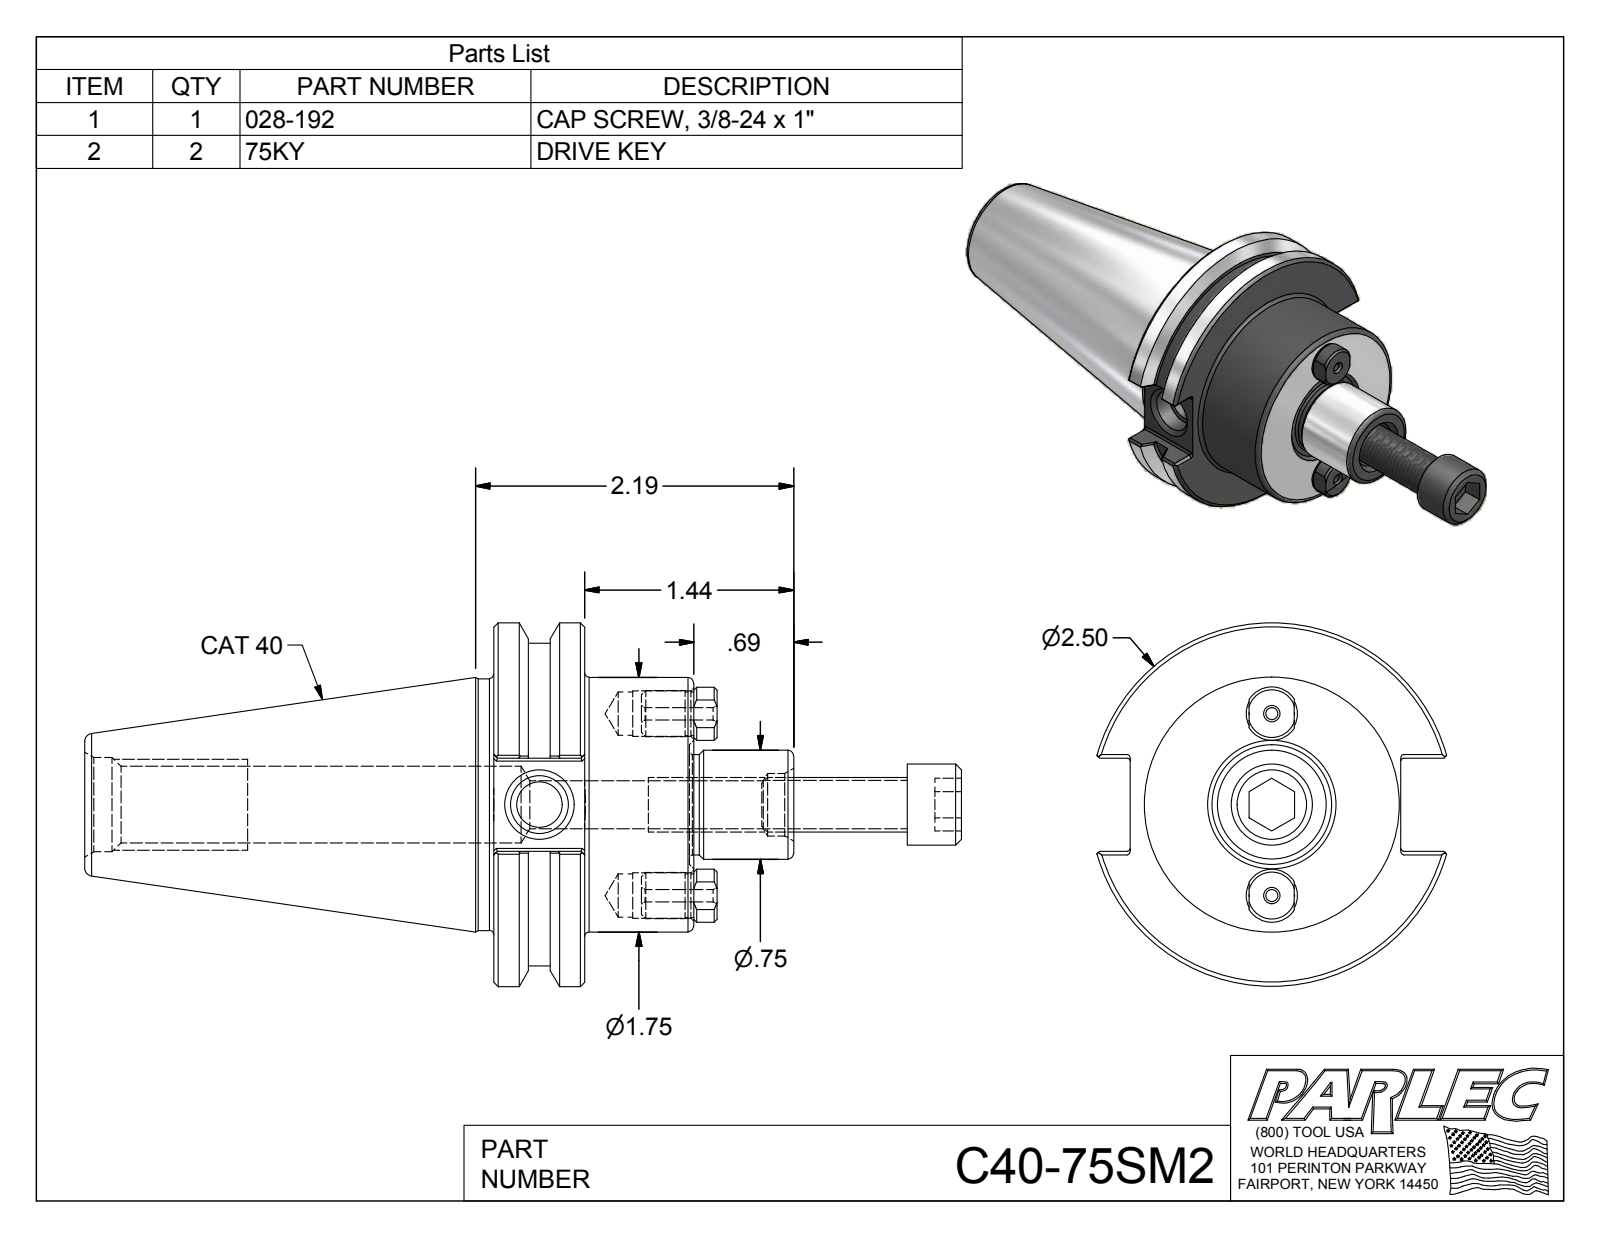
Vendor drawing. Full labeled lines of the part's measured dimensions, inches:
Part name (STEP PRODUCT): C40-75SM2; C40-75SM2-1; 75KY; 028-192
STEP written by: Autodesk Inventor 2012 (AUTOMOTIVE_DESIGN)
Units: inches
Bodies: 4 solids, 154 faces (57 planar, 44 cylindrical, 53 other)
Overall size (bounding box): 6.026 × 2.5 × 2.406
Volume: 8.318 in³ · Surface area: 43.55 in²
Round holes (diameter × count): ⌀0.084 ×2, ⌀0.297 ×2, ⌀0.312 ×2, ⌀0.315 ×1, ⌀0.33 ×1, ⌀0.399 ×1, ⌀0.43 ×1, ⌀0.527 ×1, ⌀0.648 ×1
Round bosses / shafts (diameter × count): ⌀0.318 ×2, ⌀0.3 ×2, ⌀2.5 ×1, ⌀2.219 ×1, ⌀1.75 ×1, ⌀1.73 ×1, ⌀0.75 ×1, ⌀0.69 ×1
Partial cylindrical surfaces — rounded edges, fillets, slot ends (radius × count): R0.02 ×12, R0.183 ×2
Main face-to-face distances: 0.625, 1.375, 0.75, 0.64, 0.19, 1.497, 1.86, 2.812, 3.437, 4.187
Hole centre spacings: 0.625, 0.625, 1.25
